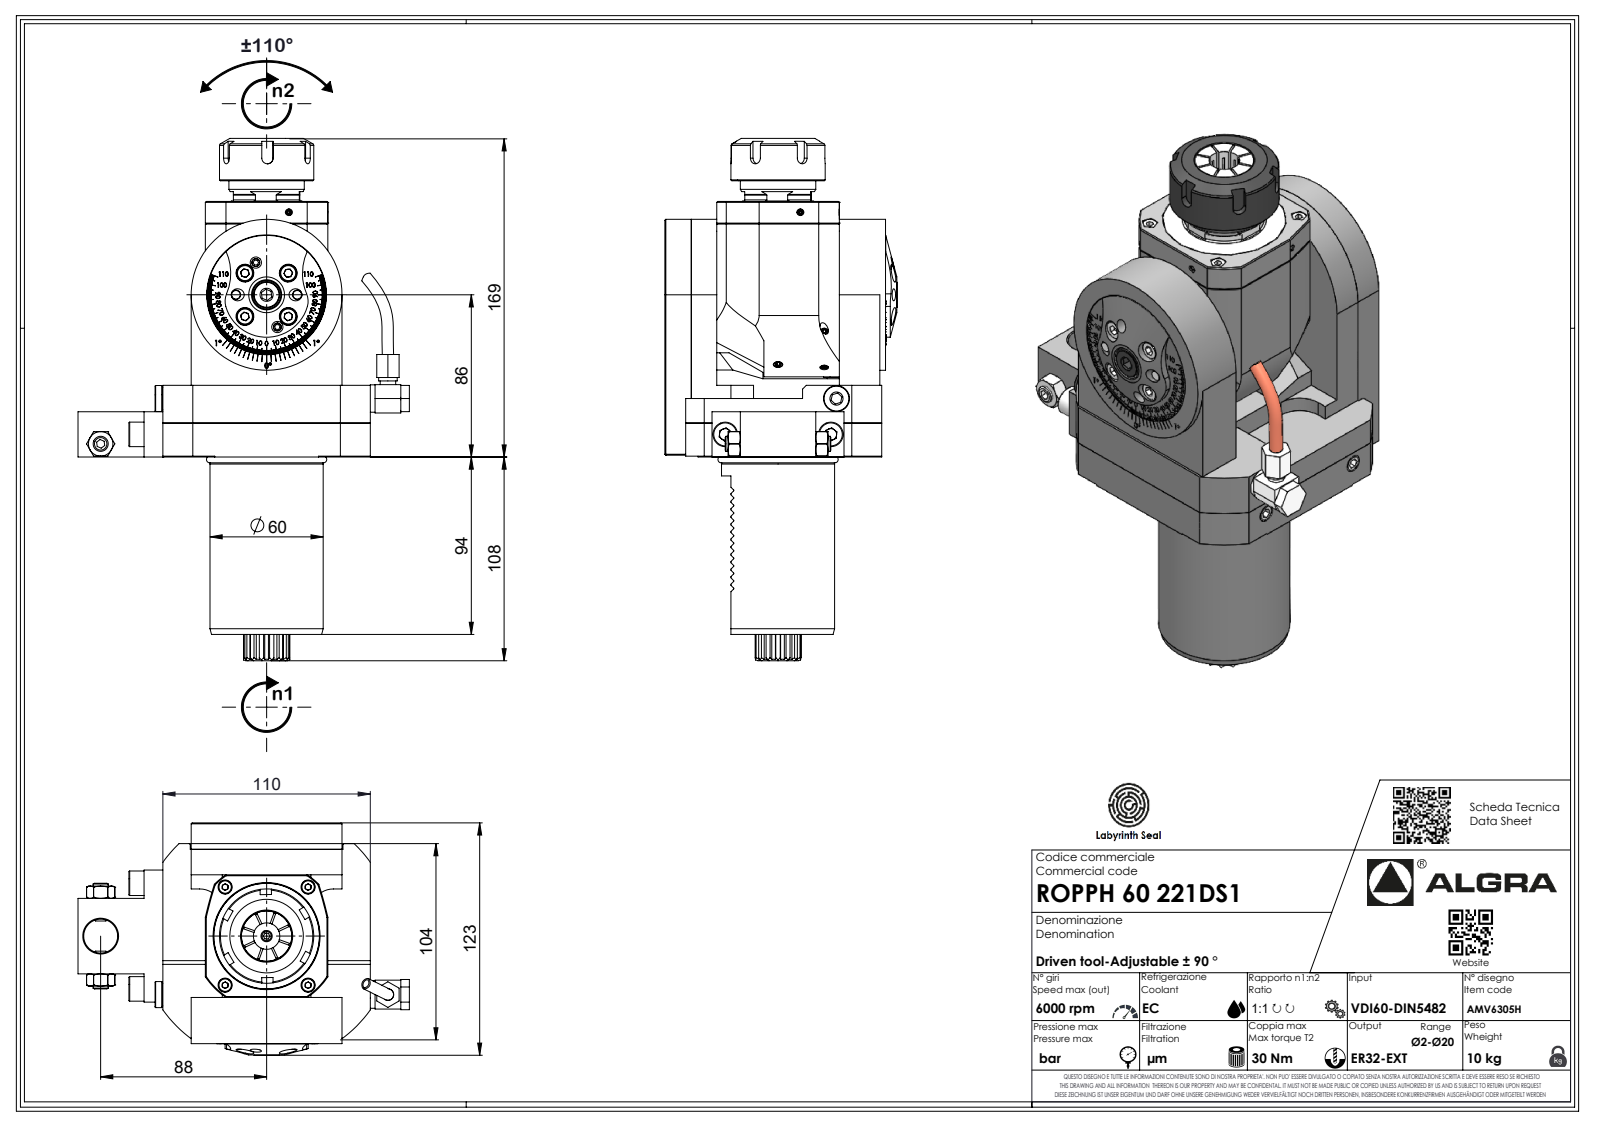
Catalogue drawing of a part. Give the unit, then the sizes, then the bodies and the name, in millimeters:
Units: millimetres
Overall size (bounding box): 276.91 × 175.7 × 123
Round holes (diameter × count): ⌀2.1 ×1, ⌀5 ×1
Round bosses / shafts (diameter × count): ⌀80 ×1, ⌀60 ×1, ⌀58.7 ×1, ⌀50 ×1, ⌀40 ×1, ⌀14.5 ×1, ⌀9.8 ×1, ⌀8.2 ×1
Partial cylindrical surfaces — rounded edges, fillets, slot ends (radius × count): R0.3 ×14, R0.33 ×7, R0.52 ×7, R3.7 ×7, R3 ×5, R0.2 ×3, R10 ×2, R12 ×2
Main face-to-face distances: 22.5, 87.5, 65, 80, 7.5, 95, 135.5, 7, 27.5, 94
Volume: 1 484 000 mm³ · Surface area: 126 917 mm²
Bodies: 1 solid, 688 faces (428 planar, 127 cylindrical, 133 other)
Part name (STEP PRODUCT): ROPPH60221DS1
STEP written by: SolidWorks 2023 (AUTOMOTIVE_DESIGN)
